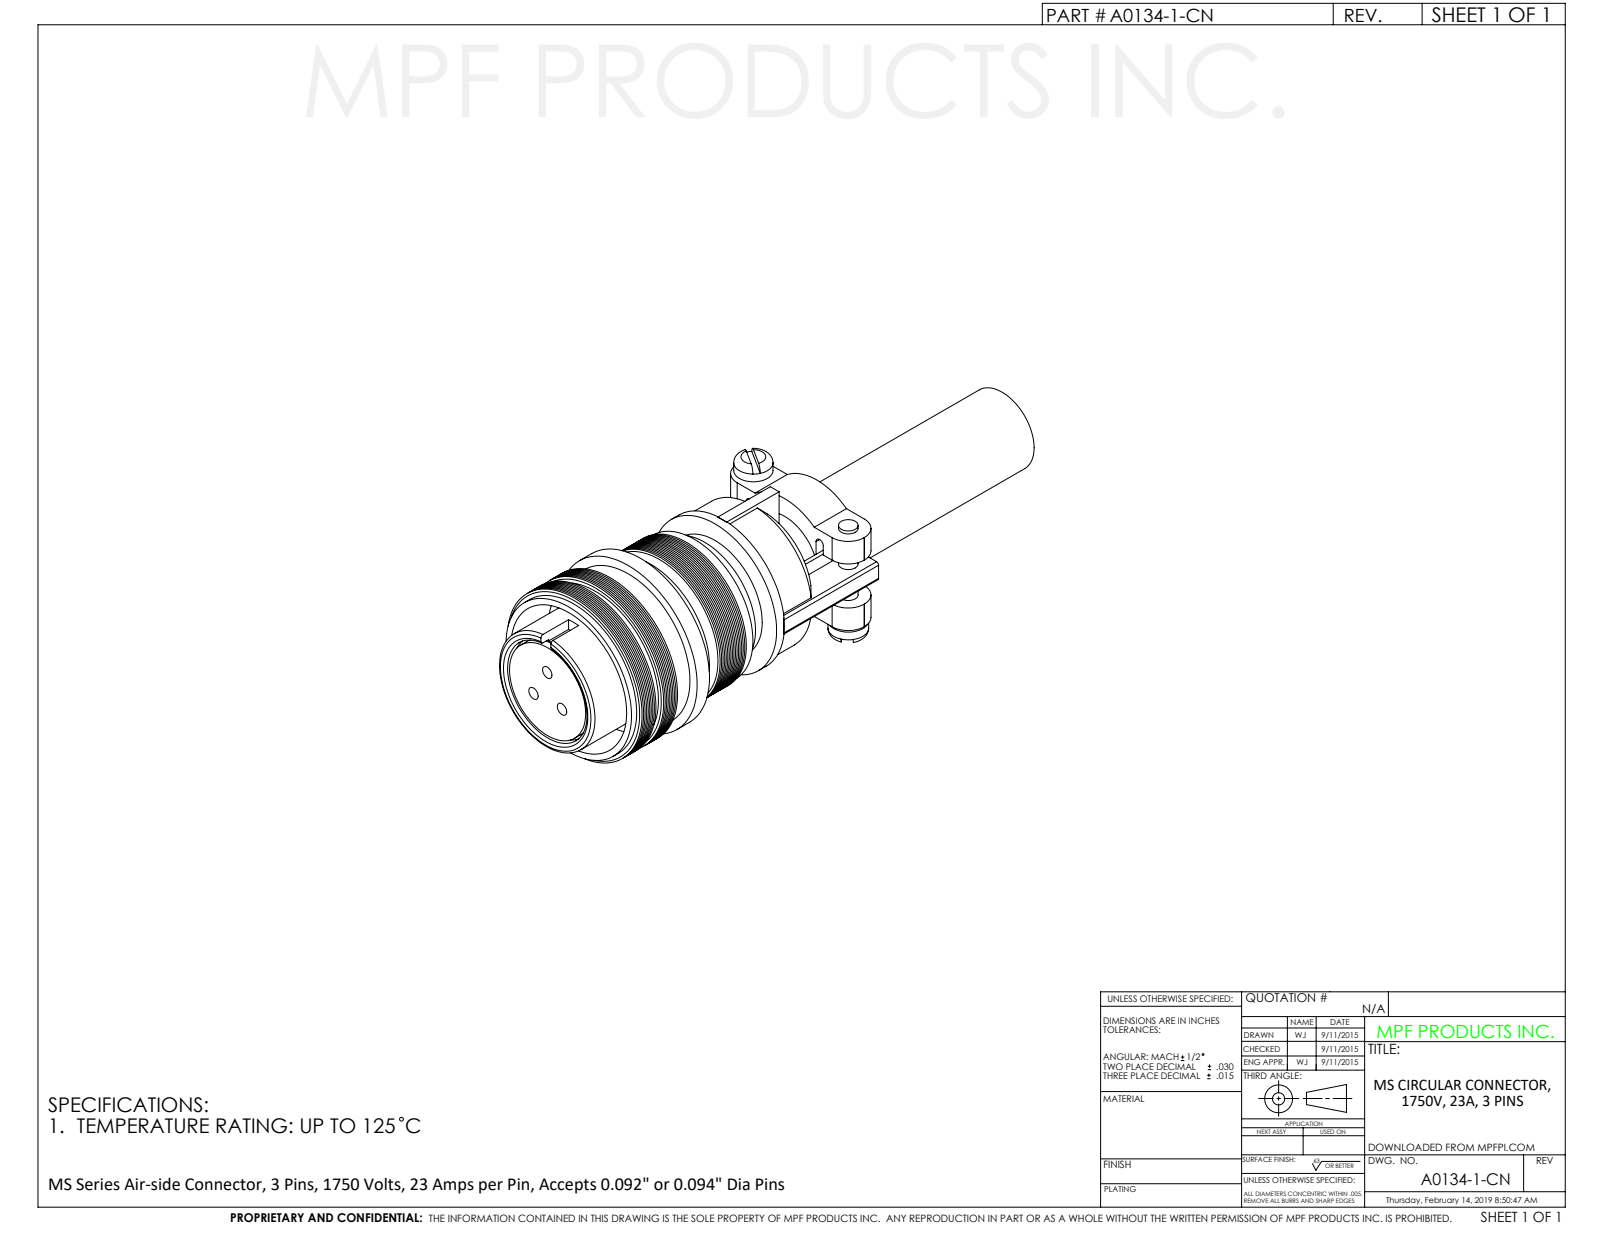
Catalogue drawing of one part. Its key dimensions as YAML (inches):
part_name: "A0134-1-CN"
step_written_by: "SolidWorks 2012 (CONFIG_CONTROL_DESIGN)"
units: inches
bodies: {solids: 1, faces: 373, planar: 106, cylindrical: 85, other: 182}
overall_size: [4.437, 1.34, 1.34]
volume: 2.393
surface_area: 31.42
round_holes:
  - {diameter: 0.091, count: 3}
  - {diameter: 0.55, count: 1}
  - {diameter: 0.78, count: 1}
  - {diameter: 1.125, count: 1}
round_bosses_or_shafts:
  - {diameter: 0.135, count: 2}
  - {diameter: 1.34, count: 1}
  - {diameter: 1.223, count: 1}
  - {diameter: 1.22, count: 1}
  - {diameter: 1.2, count: 1}
  - {diameter: 1.14, count: 1}
  - {diameter: 0.99, count: 1}
  - {diameter: 0.92, count: 1}
partial_cylinders:
  - {radius: 0.034, count: 8}
  - {radius: 0.02, count: 4}
  - {radius: 0.156, count: 4}
  - {radius: 0.323, count: 1}
  - {radius: 0.472, count: 1}
  - {radius: 0.473, count: 1}
face_to_face_distances: [1.193, 0.643, 0.47, 0.722, 0.1, 0.2, 2.096, 1.626, 0.904, 0.522]
hole_center_spacings: [0.277, 0.16, 0.16]
